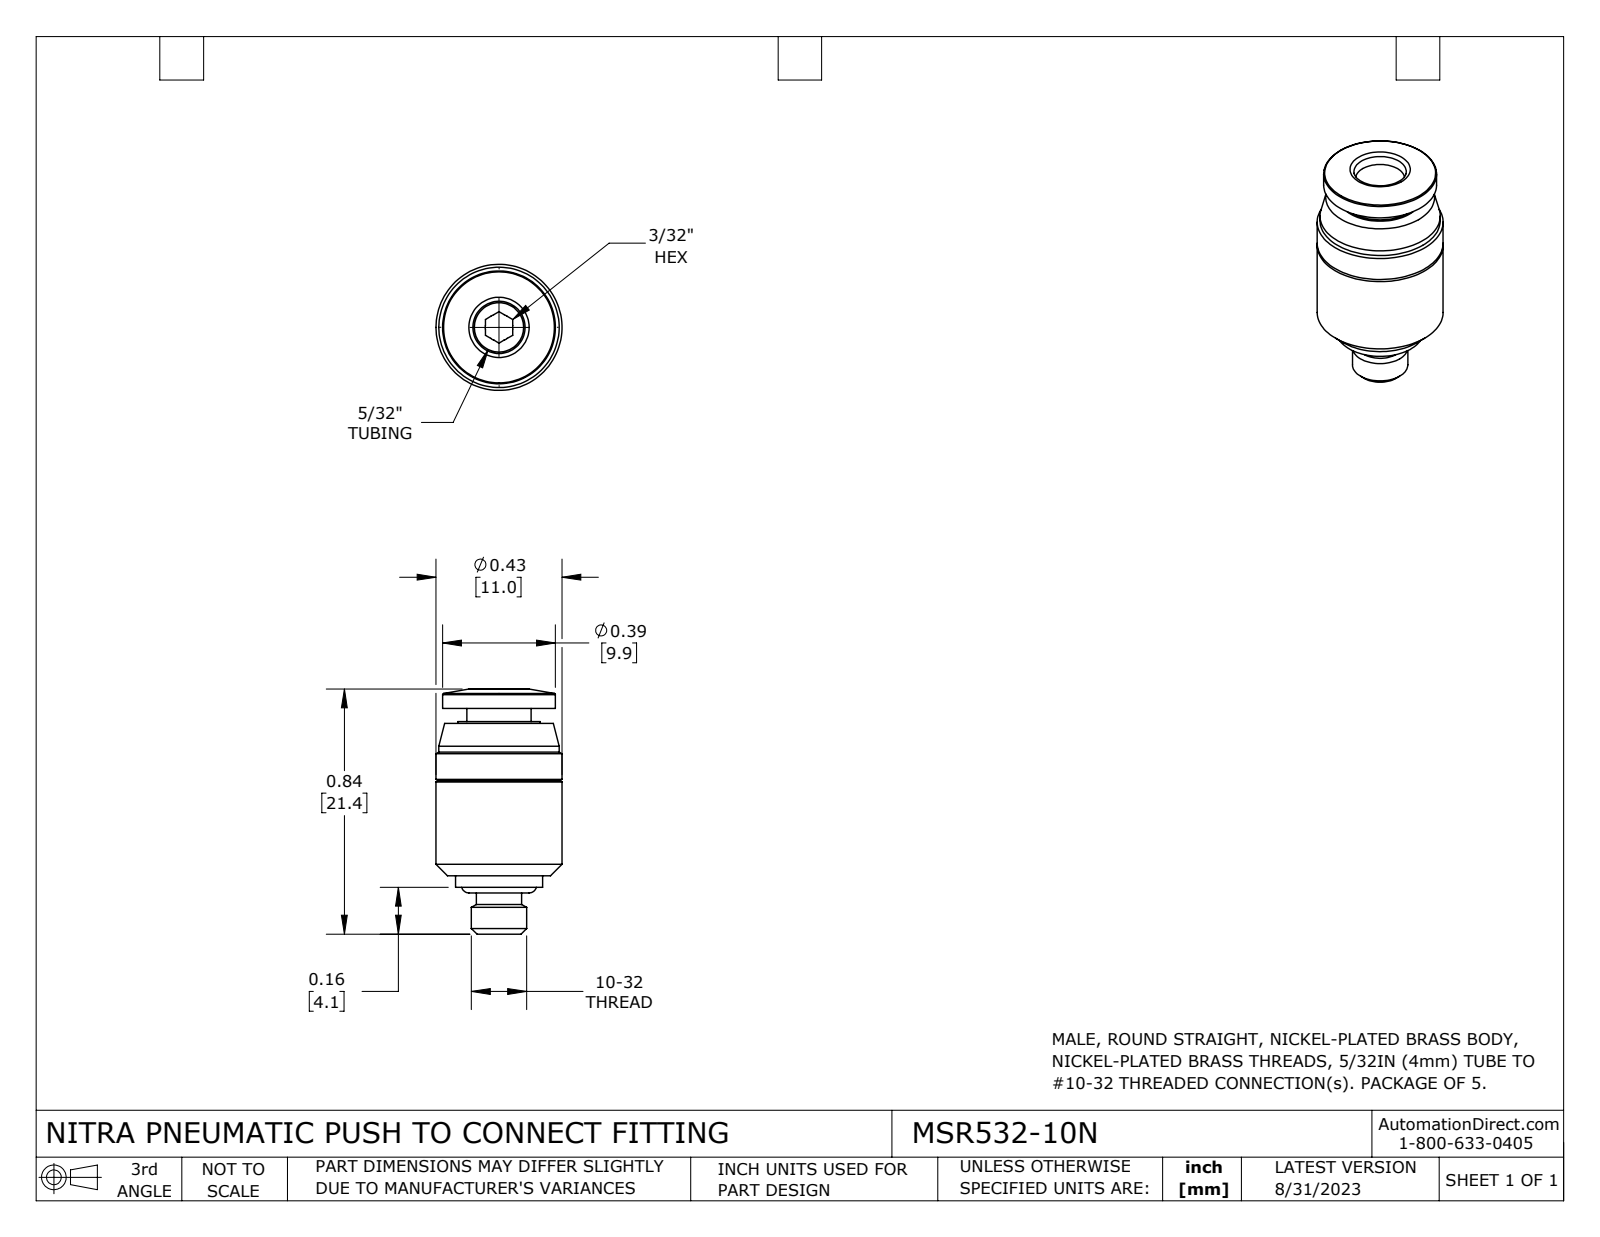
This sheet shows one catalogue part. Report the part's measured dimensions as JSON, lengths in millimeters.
{"part_name": "MSR532-10N", "step_written_by": "SolidWorks 2015 (AUTOMOTIVE_DESIGN)", "units": "millimeters", "bodies": {"solids": 2, "faces": 63, "planar": 9, "cylindrical": 24, "other": 30}, "overall_size": [21.4, 11, 11], "volume_mm3": 1200, "surface_area_mm2": 1189, "round_holes": [[2.4, 1], [4.3, 1]], "round_bosses_or_shafts": [[11, 1], [10.5, 1], [9.9, 1], [7.6, 1], [7.2, 1], [5.6, 1], [4.8, 1], [4, 1]], "face_to_face_distances": [1.3, 13.3, 14.6, 13.5, 14.8, 13.6, 13.5, 1.1, 1.7, 1.5]}
